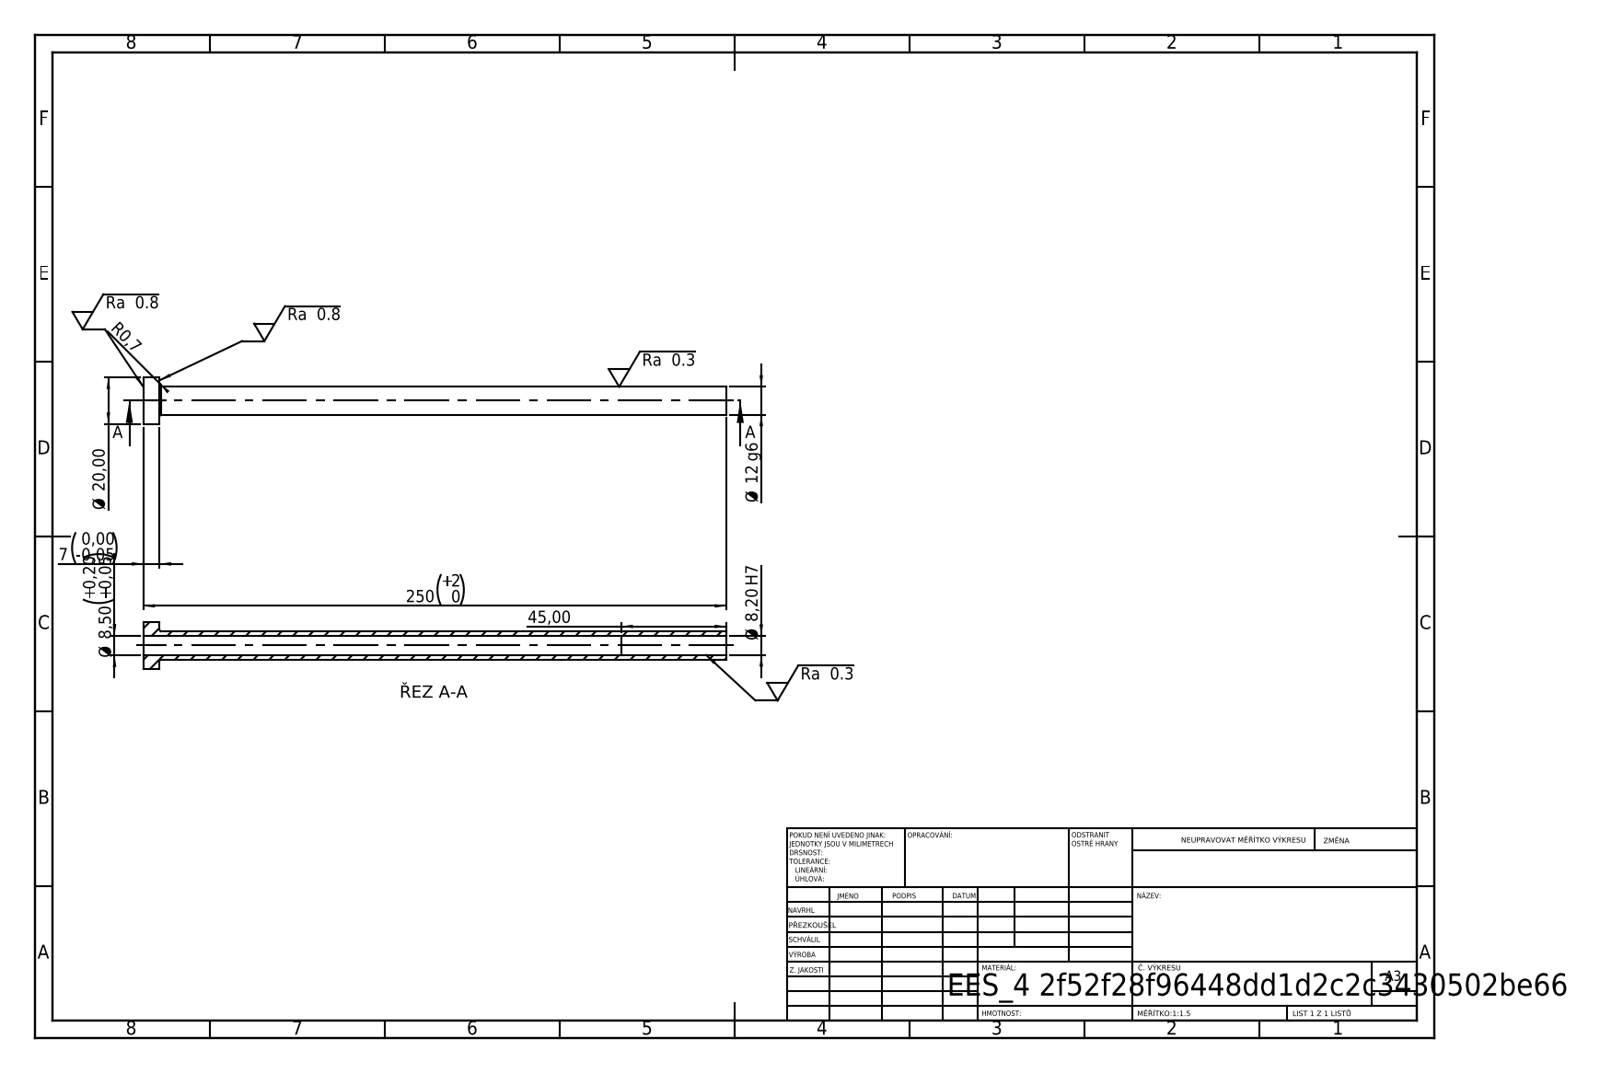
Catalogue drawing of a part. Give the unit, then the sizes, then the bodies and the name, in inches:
Units: inches
Overall size (bounding box): 9.843 × 0.787 × 0.787
Round holes (diameter × count): ⌀0.323 ×1, ⌀0.335 ×1
Round bosses / shafts (diameter × count): ⌀0.787 ×1, ⌀0.472 ×1
Main face-to-face distances: 0.276, 9.843, 9.567, 8.071, 7.795, 1.772
Volume: 0.957 in³ · Surface area: 25.96 in²
Bodies: 1 solid, 14 faces (4 planar, 8 cylindrical, 2 other)
STEP written by: SolidWorks 2019 (CONFIG_CONTROL_DESIGN)
